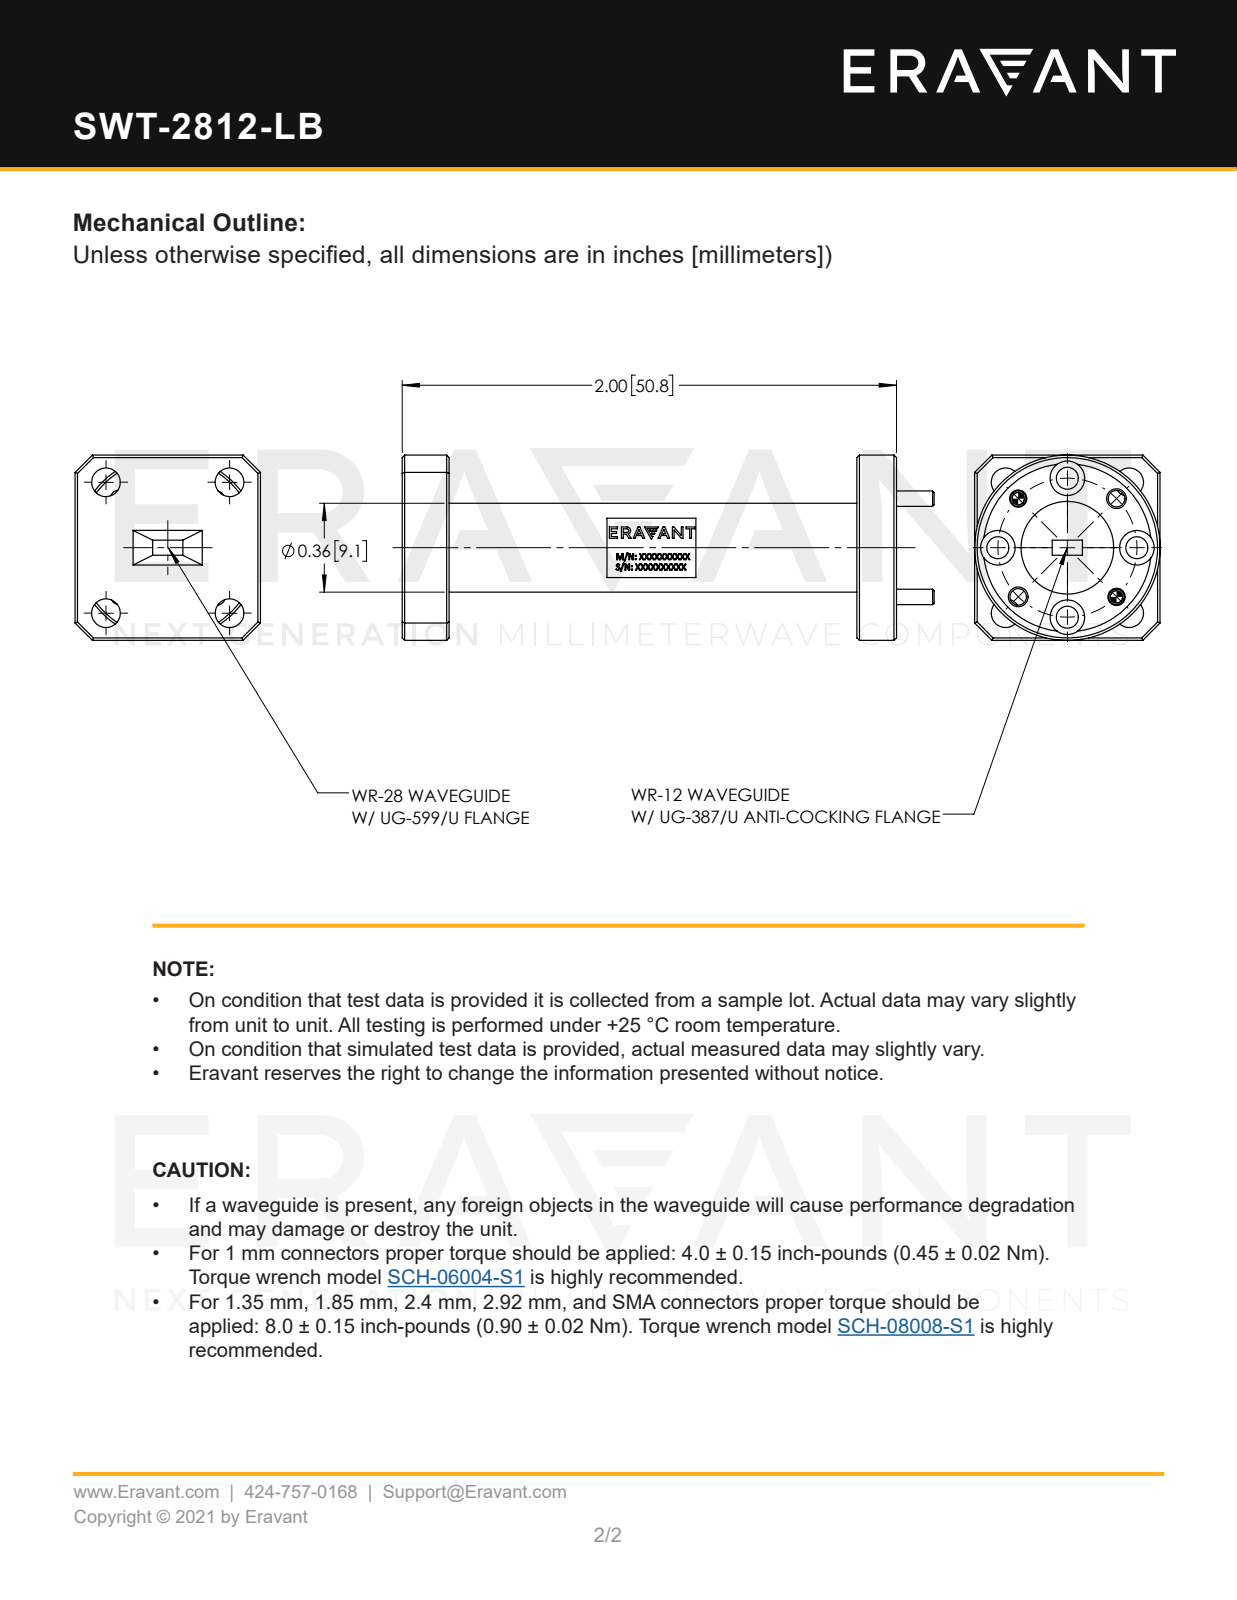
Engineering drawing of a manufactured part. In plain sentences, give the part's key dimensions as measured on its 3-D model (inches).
The part is named "SWT-2812-LB". Its 3-D file was written by "SolidWorks 2021 (CONFIG_CONTROL_DESIGN)". It is 3 solids with 114 faces: 48 planar, 46 cylindrical and 20 other. Overall it measures 2.153 by 0.75 by 0.75 inches. Its volume is 0.325 cubic inches and its surface area 5.126 square inches. Round holes: 4 of diameter 0.089, 4 of diameter 0.116, 4 of diameter 0.14, 2 of diameter 0.061, 2 of diameter 0.067, 1 of diameter 0.68. Round bosses or shafts: 2 of diameter 0.063, 1 of diameter 0.75, 1 of diameter 0.375, 1 of diameter 0.36. The main face-to-face distances are 0.19, 1.65, 1.84, 0.75, 1.98, 0.14, 1.79, 0.02, 0.16, 1.81. The hole center spacings are 0.215, 0.52, 0.398, 0.083, 0.25, 0.281, 0.281, 0.454.
